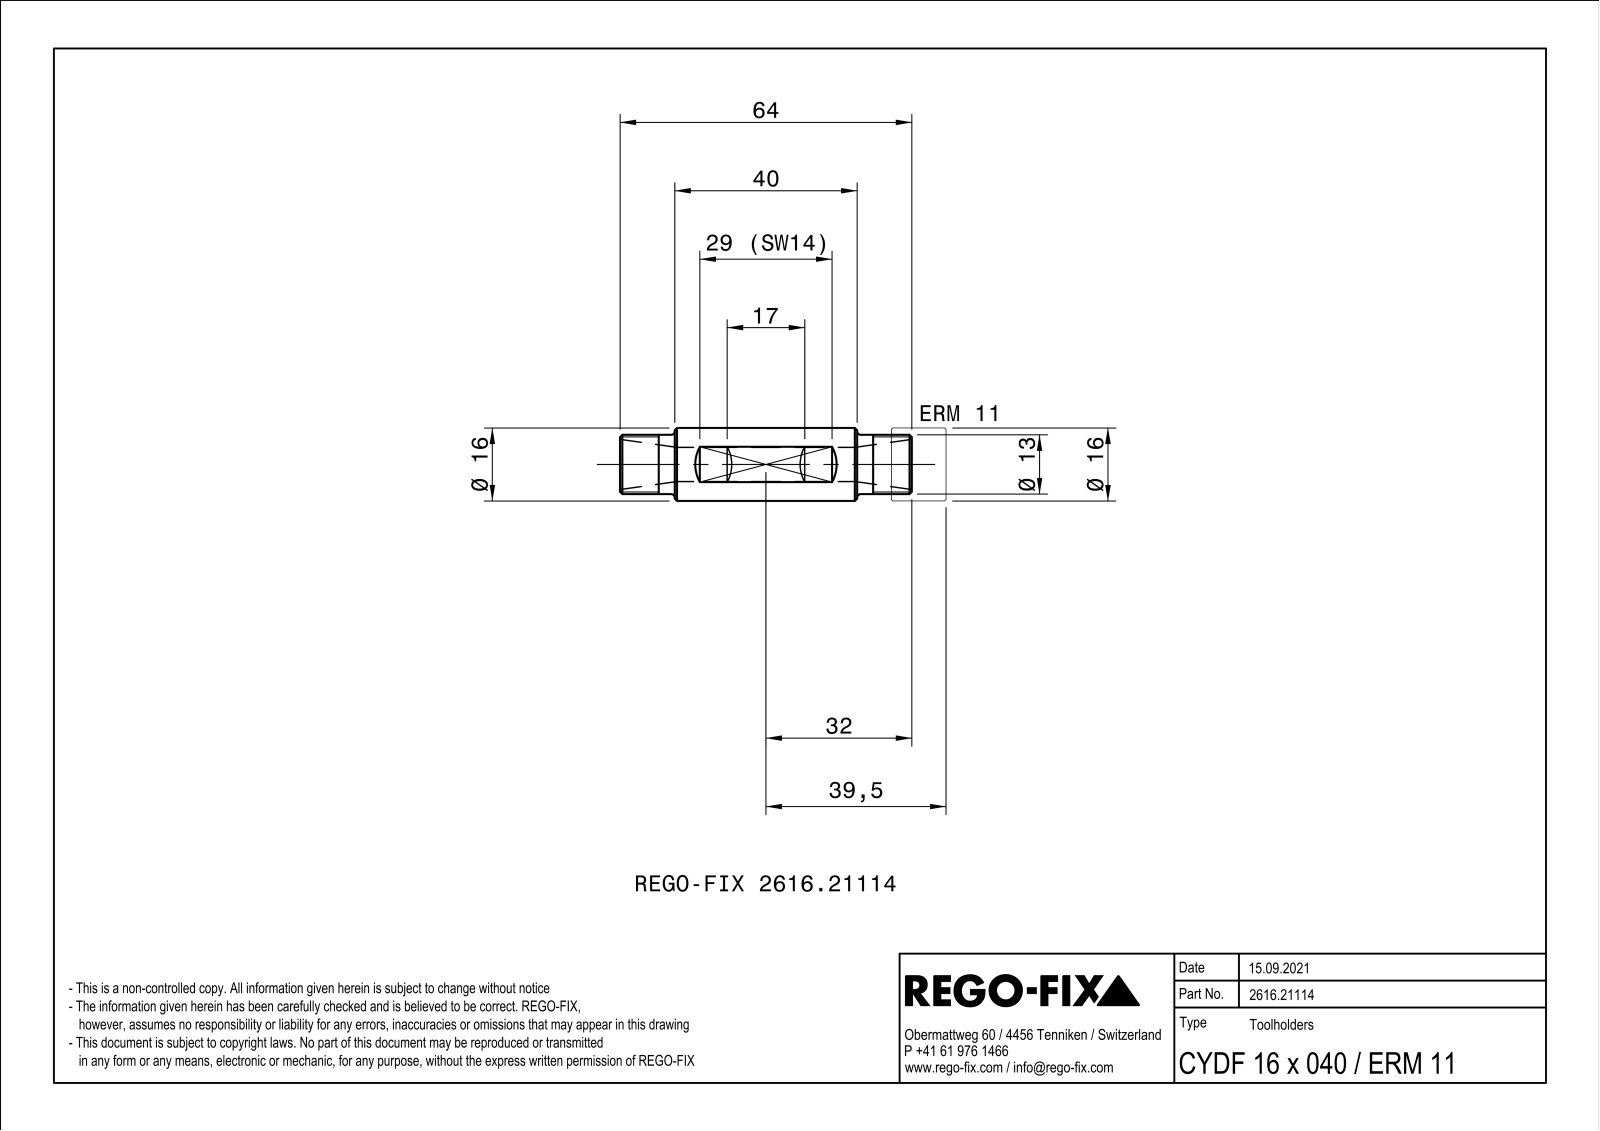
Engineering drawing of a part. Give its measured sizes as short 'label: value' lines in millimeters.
name: NOCUT
written by: SIEMENS PLM Software Solid Edge ST10 (AUTOMOTIVE_DESIGN)
unit: mm
bodies: 1 solid, 29 faces (13 planar, 6 cylindrical, 10 other)
size: 64 × 16 × 16
volume: 7 568 mm³; area: 4 765 mm²
holes: 1× ⌀7.5
bosses: 1× ⌀16, 1× ⌀13
face distances: 14, 12, 52, 5.66, 16.26, 10.6, 64, 40
